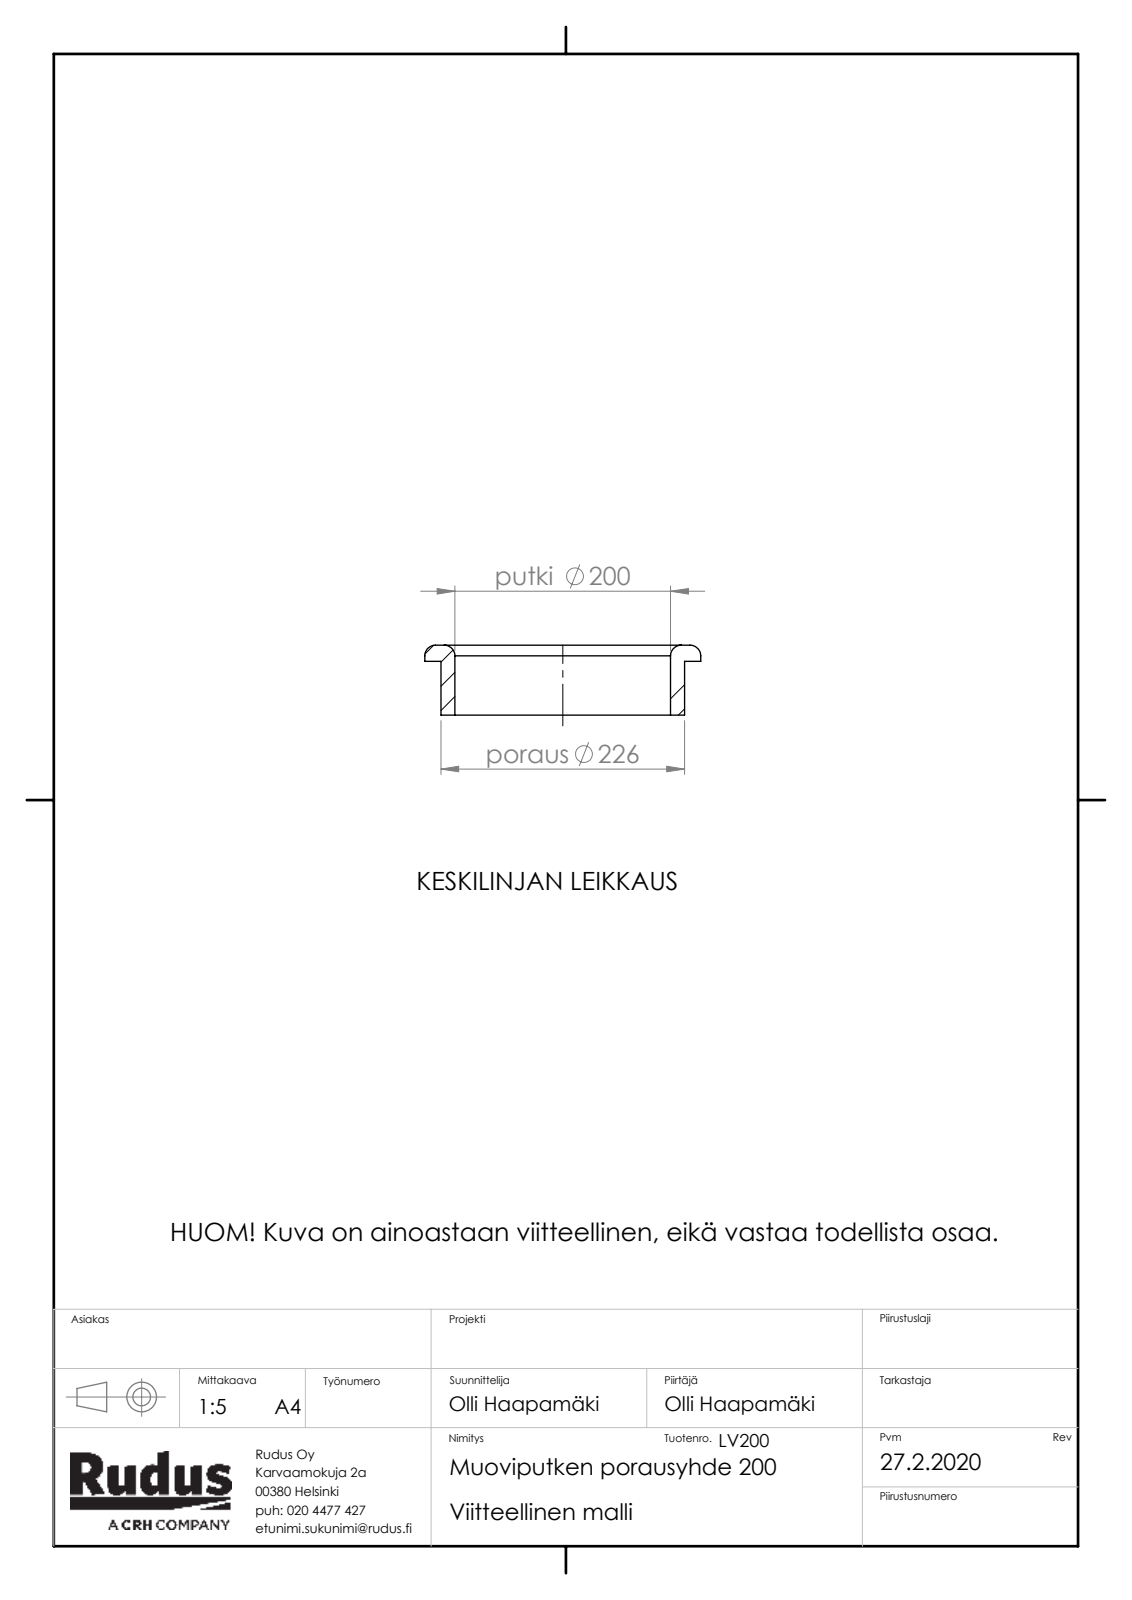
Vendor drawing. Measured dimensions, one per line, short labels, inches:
name: Rudus LV200 Muoviputken porausyhde 200; kaivo-muovi-lapivienti
written by: SolidWorks 2019 (CONFIG_CONTROL_DESIGN)
unit: in
bodies: 1 solid, 13 faces (3 planar, 6 cylindrical, 4 other)
size: 10.079 × 10.079 × 2.559
volume: 43.02 in³; area: 189.7 in²
holes: 1× ⌀7.874
bosses: 1× ⌀10.079, 1× ⌀8.898
face distances: 1.969, 2.559, 0.591
